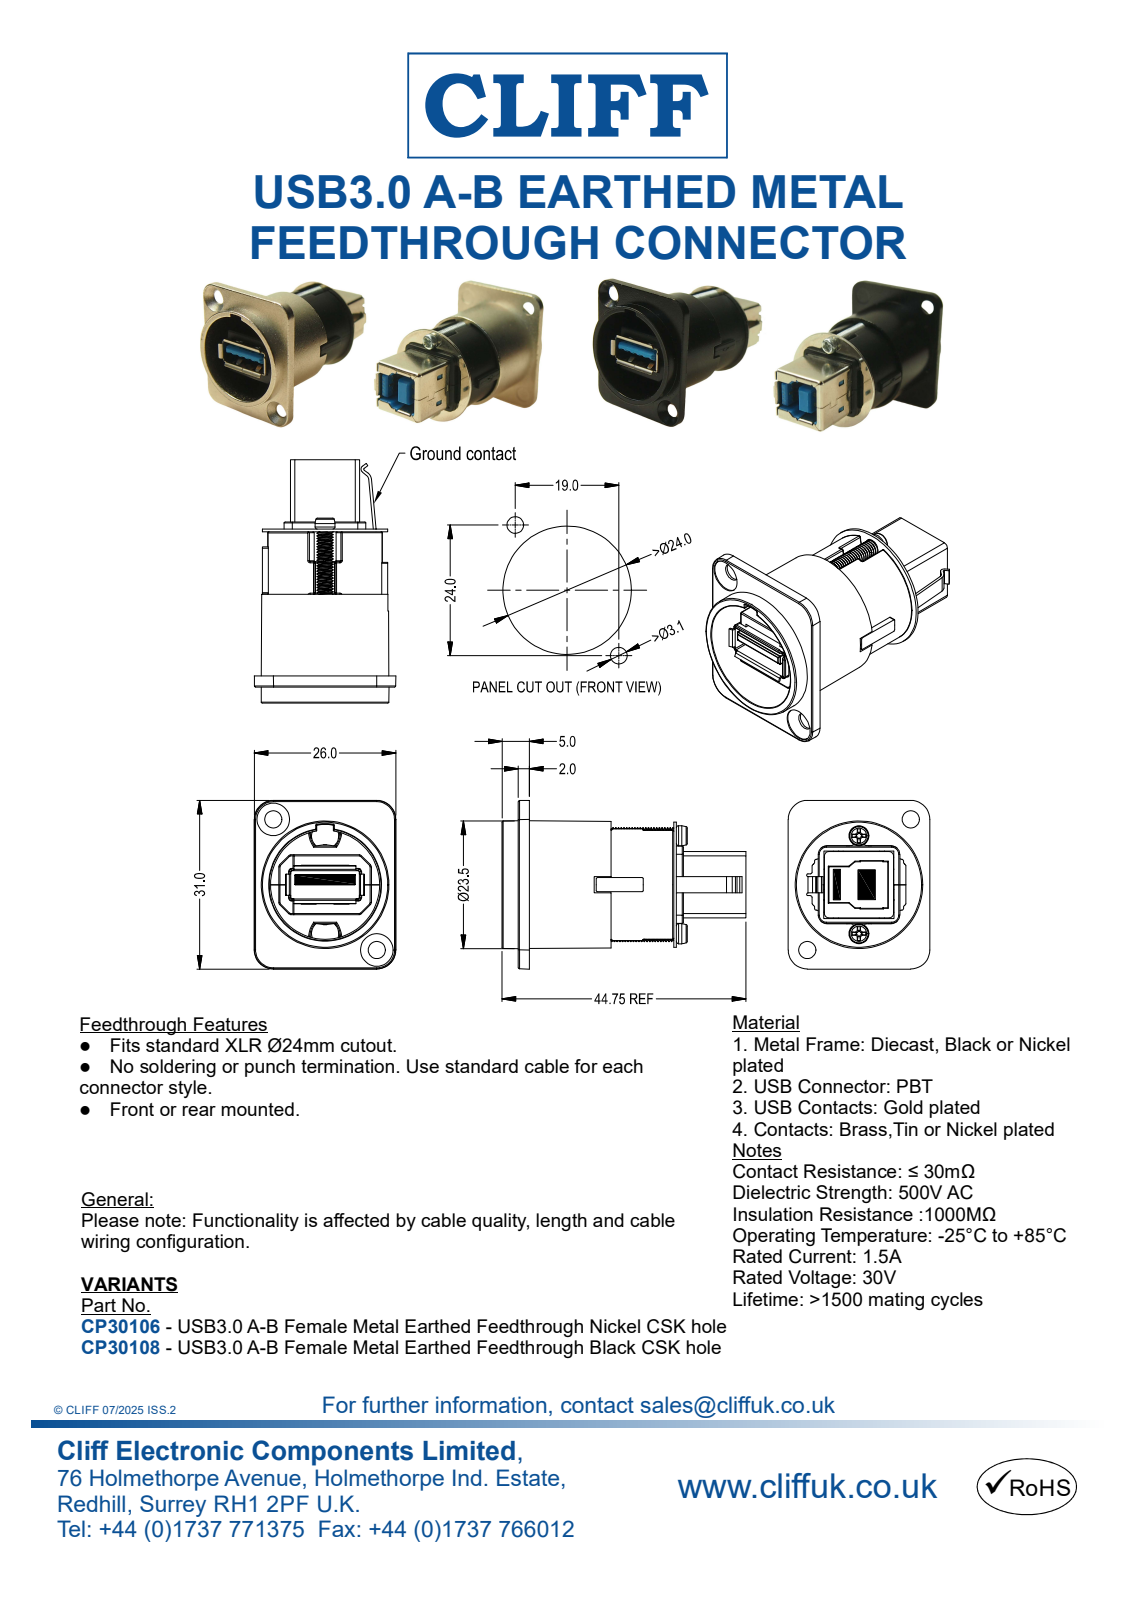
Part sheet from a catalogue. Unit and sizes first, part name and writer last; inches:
Units: inches
Overall size (bounding box): 1.762 × 1.22 × 1.024
Round holes (diameter × count): ⌀0.102 ×2, ⌀0.126 ×2, ⌀0.236 ×2, ⌀0.035 ×1
Round bosses / shafts (diameter × count): ⌀0.146 ×2, ⌀0.114 ×2, ⌀0.906 ×1, ⌀0.827 ×1
Partial cylindrical surfaces — rounded edges, fillets, slot ends (radius × count): R0.008 ×52, R0.004 ×32, R0.012 ×30, R0.02 ×15, R0.059 ×9, R0.024 ×8, R0.039 ×6, R0.016 ×4
Main face-to-face distances: 0.126, 0.102, 0.114, 0.217, 0.358, 0.138, 0.016, 0.122, 0.098, 0.354
Hole centre spacings: 0.392, 0.907, 0.709, 1.205
Volume: 0.566 in³ · Surface area: 19.2 in²
Bodies: 1 solid, 1243 faces (667 planar, 329 cylindrical, 247 other)
STEP written by: Autodesk Inventor 2022 (AUTOMOTIVE_DESIGN)
